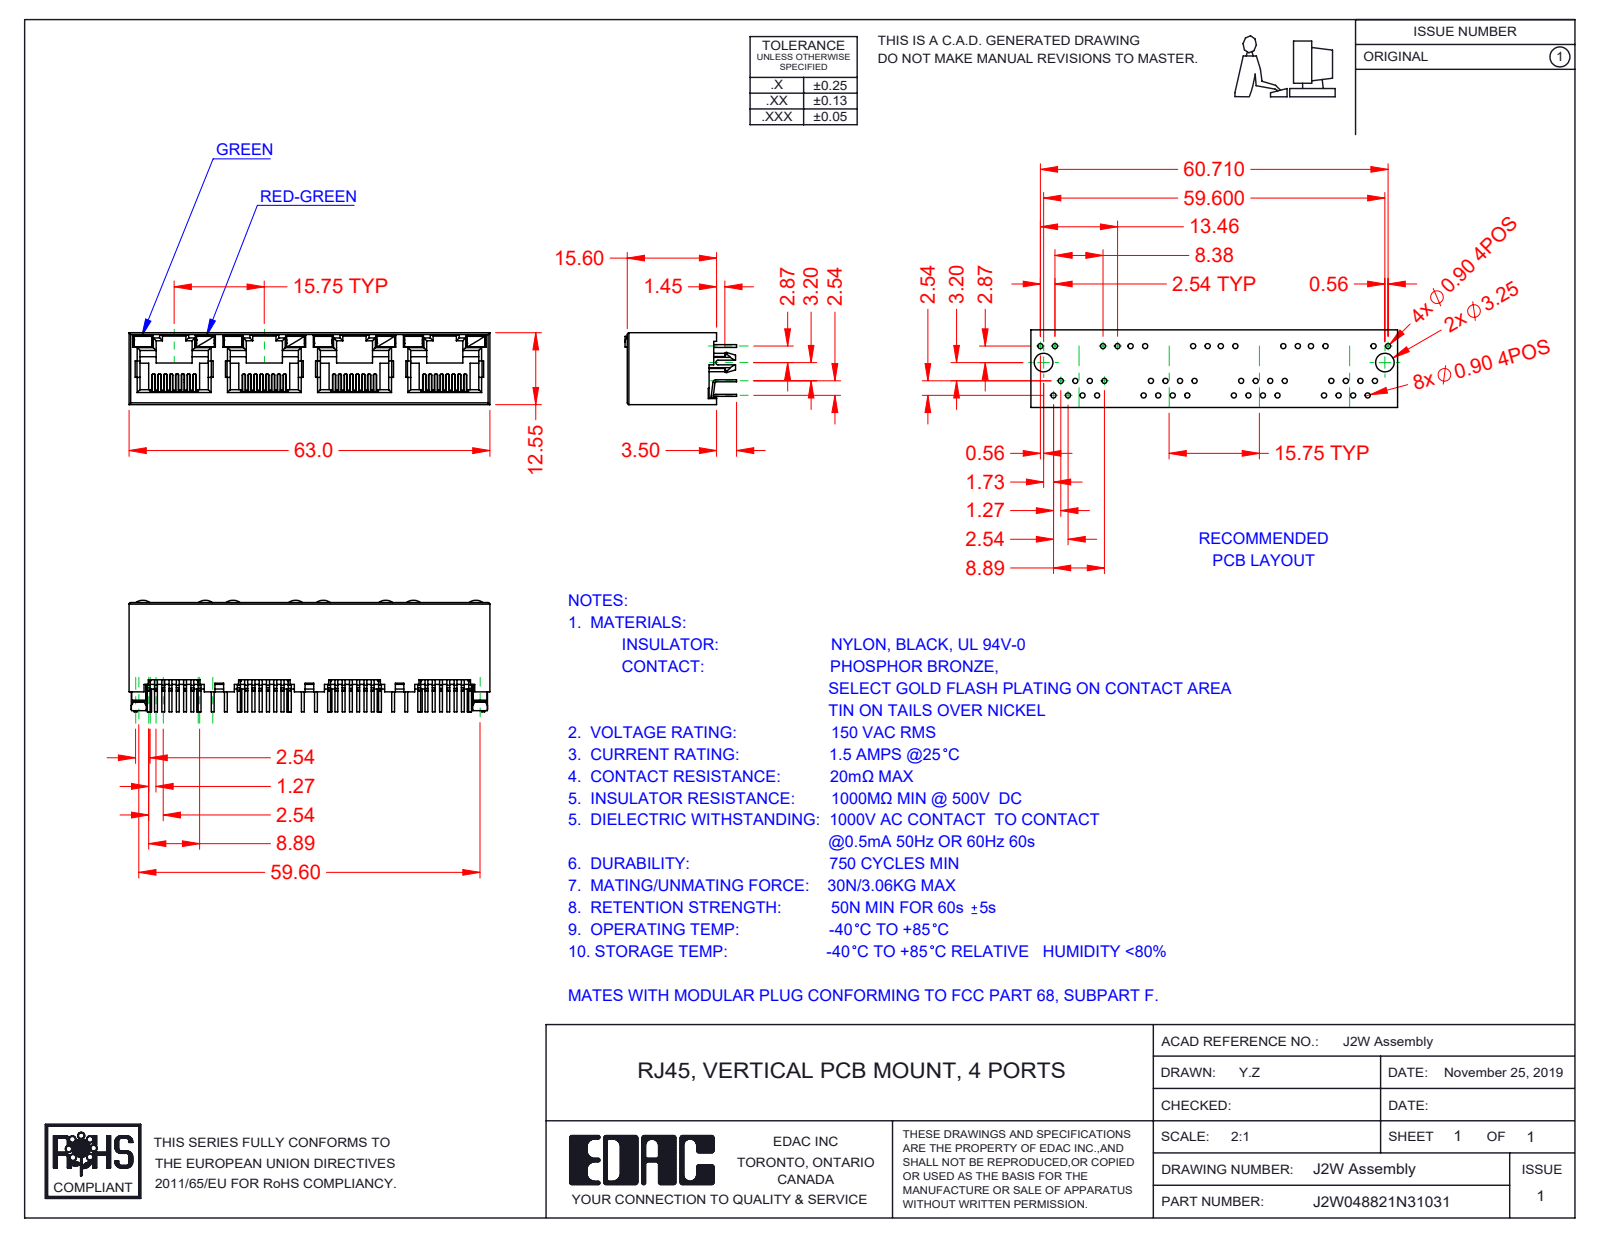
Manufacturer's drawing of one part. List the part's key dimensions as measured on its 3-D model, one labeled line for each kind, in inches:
Part name (STEP PRODUCT): 2W LED LH_3-Green; 2W Contact Lock; 2W Contacts; 2W Insulator (+2 more)
STEP written by: SolidWorks 2016 (CONFIG_CONTROL_DESIGN)
Units: inches
Bodies: 45 solids, 3139 faces (2600 planar, 481 cylindrical, 58 other)
Overall size (bounding box): 2.48 × 0.768 × 0.494
Volume: 0.326 in³ · Surface area: 20.37 in²
Partial cylindrical surfaces — rounded edges, fillets, slot ends (radius × count): R0.006 ×64, R0.008 ×29, R0.02 ×28, R0.012 ×14, R0.018 ×8, R0.079 ×8, R0.01 ×2, R0.059 ×2
Main face-to-face distances: 0.494, 0.469, 0.026, 0.62, 0.014, 0.059, 0.031, 0.024, 0.445, 1.24
